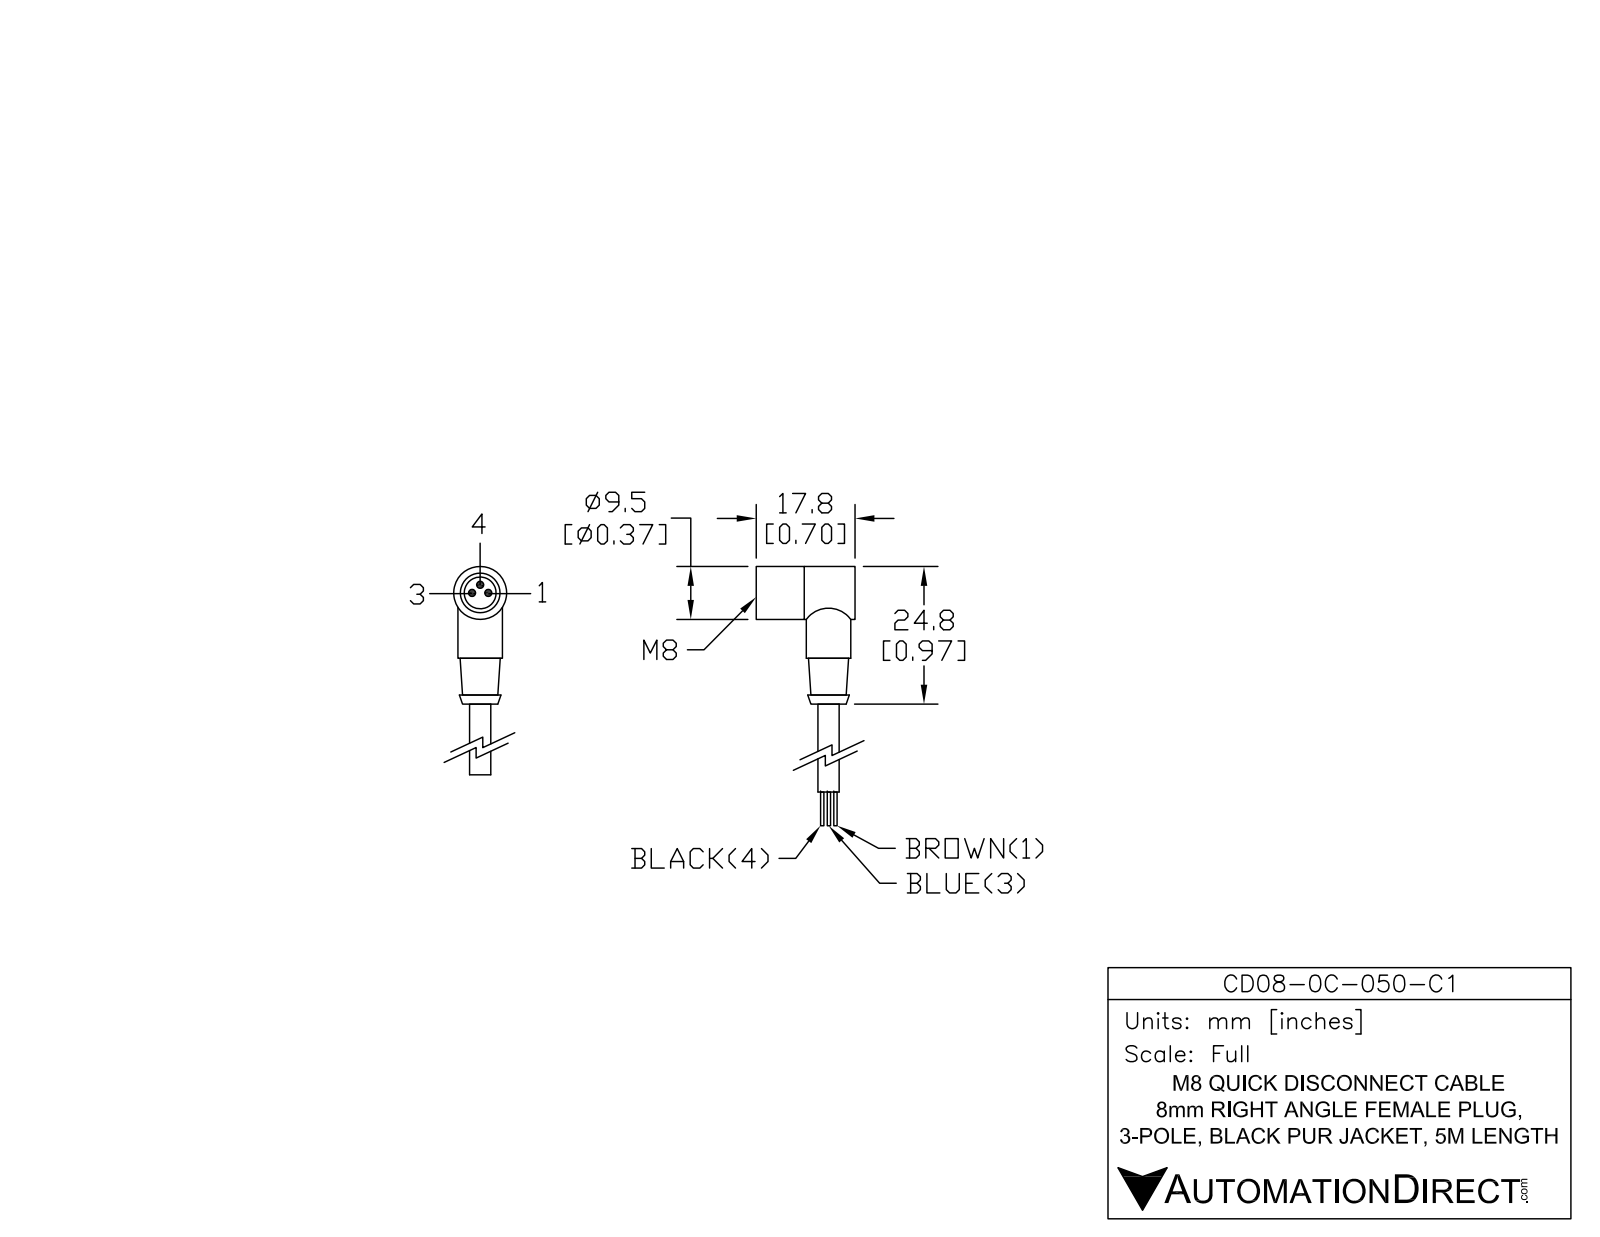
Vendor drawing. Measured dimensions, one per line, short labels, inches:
name: CD08-0C-050-C1
written by: SolidWorks 2017 (AUTOMOTIVE_DESIGN)
unit: in
bodies: 4 solids, 307 faces (222 planar, 82 cylindrical, 3 other)
size: 5.063 × 0.752 × 0.394
volume: 0.261 in³; area: 5.112 in²
holes: 3× ⌀0.035, 1× ⌀0.22, 1× ⌀0.315
bosses: 2× ⌀0.394, 1× ⌀0.26, 1× ⌀0.217, 1× ⌀0.189
rounds: 1× R0.02, 1× R0.193
face distances: 0.354, 0.024, 0.181, 0.122, 0.157, 0.28, 0.303, 3.937, 0.098, 0.205
hole spacings: 0.063, 0.089, 0.126
